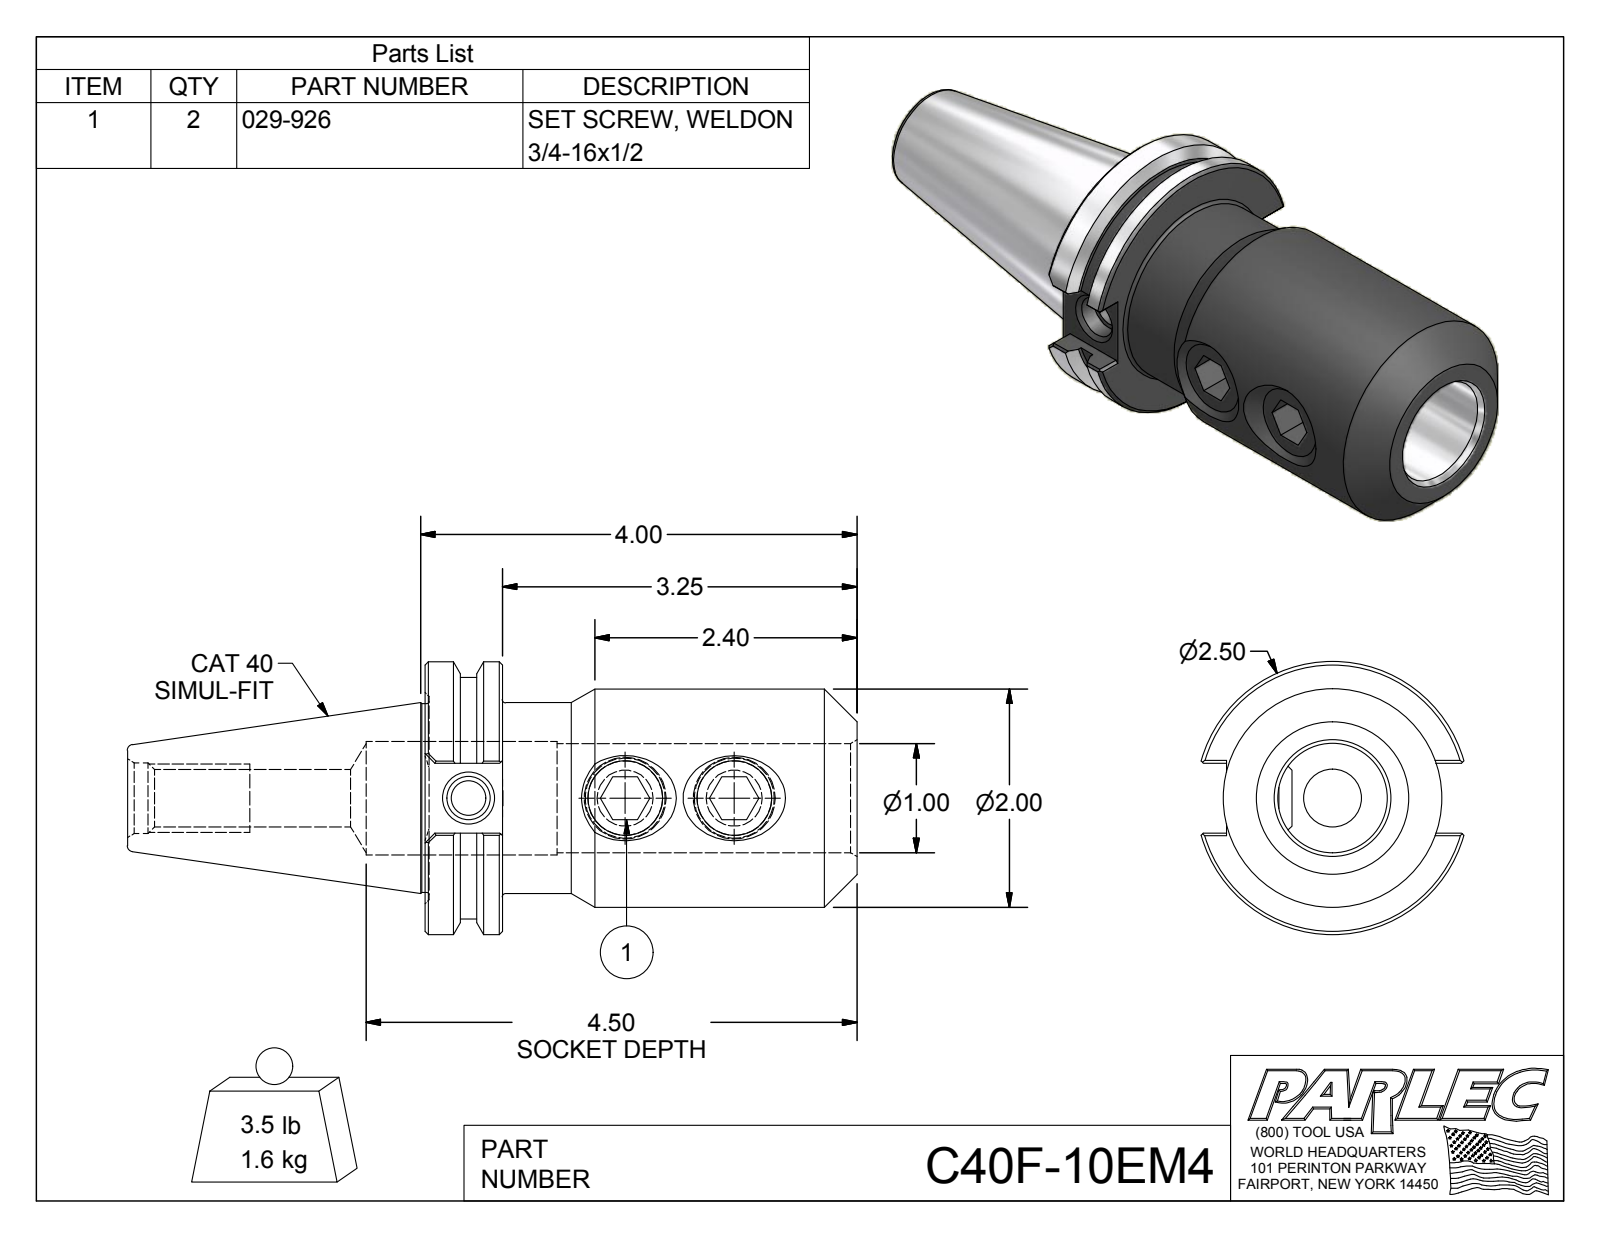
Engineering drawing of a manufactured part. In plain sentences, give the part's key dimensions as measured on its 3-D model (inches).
The part is named "C40F-10EM4; C40F-10EM4-1; 029-926". Its 3-D file was written by "Autodesk Inventor 2012 (AUTOMOTIVE_DESIGN)". It is 3 solids with 103 faces: 52 planar, 19 cylindrical and 32 other. Overall it measures 6.688 by 2.5 by 2.406 inches. Its volume is 12.17 cubic inches and its surface area 69.07 square inches. Round holes: 2 of diameter 0.682, 1 of diameter 0.315, 1 of diameter 0.399, 1 of diameter 0.527, 1 of diameter 0.648, 1 of diameter 1, 1 of diameter 1.04. Round bosses or shafts: 2 of diameter 0.75, 1 of diameter 2.5, 1 of diameter 2.215, 1 of diameter 2, 1 of diameter 1.75, 1 of diameter 1.73. The main face-to-face distances are 0.711, 0.394, 3.961, 3.25, 0.472, 0.5, 1.76, 0.866, 0.123, 0.517. The hole center spacings are 1, 1.435, 2.435.
